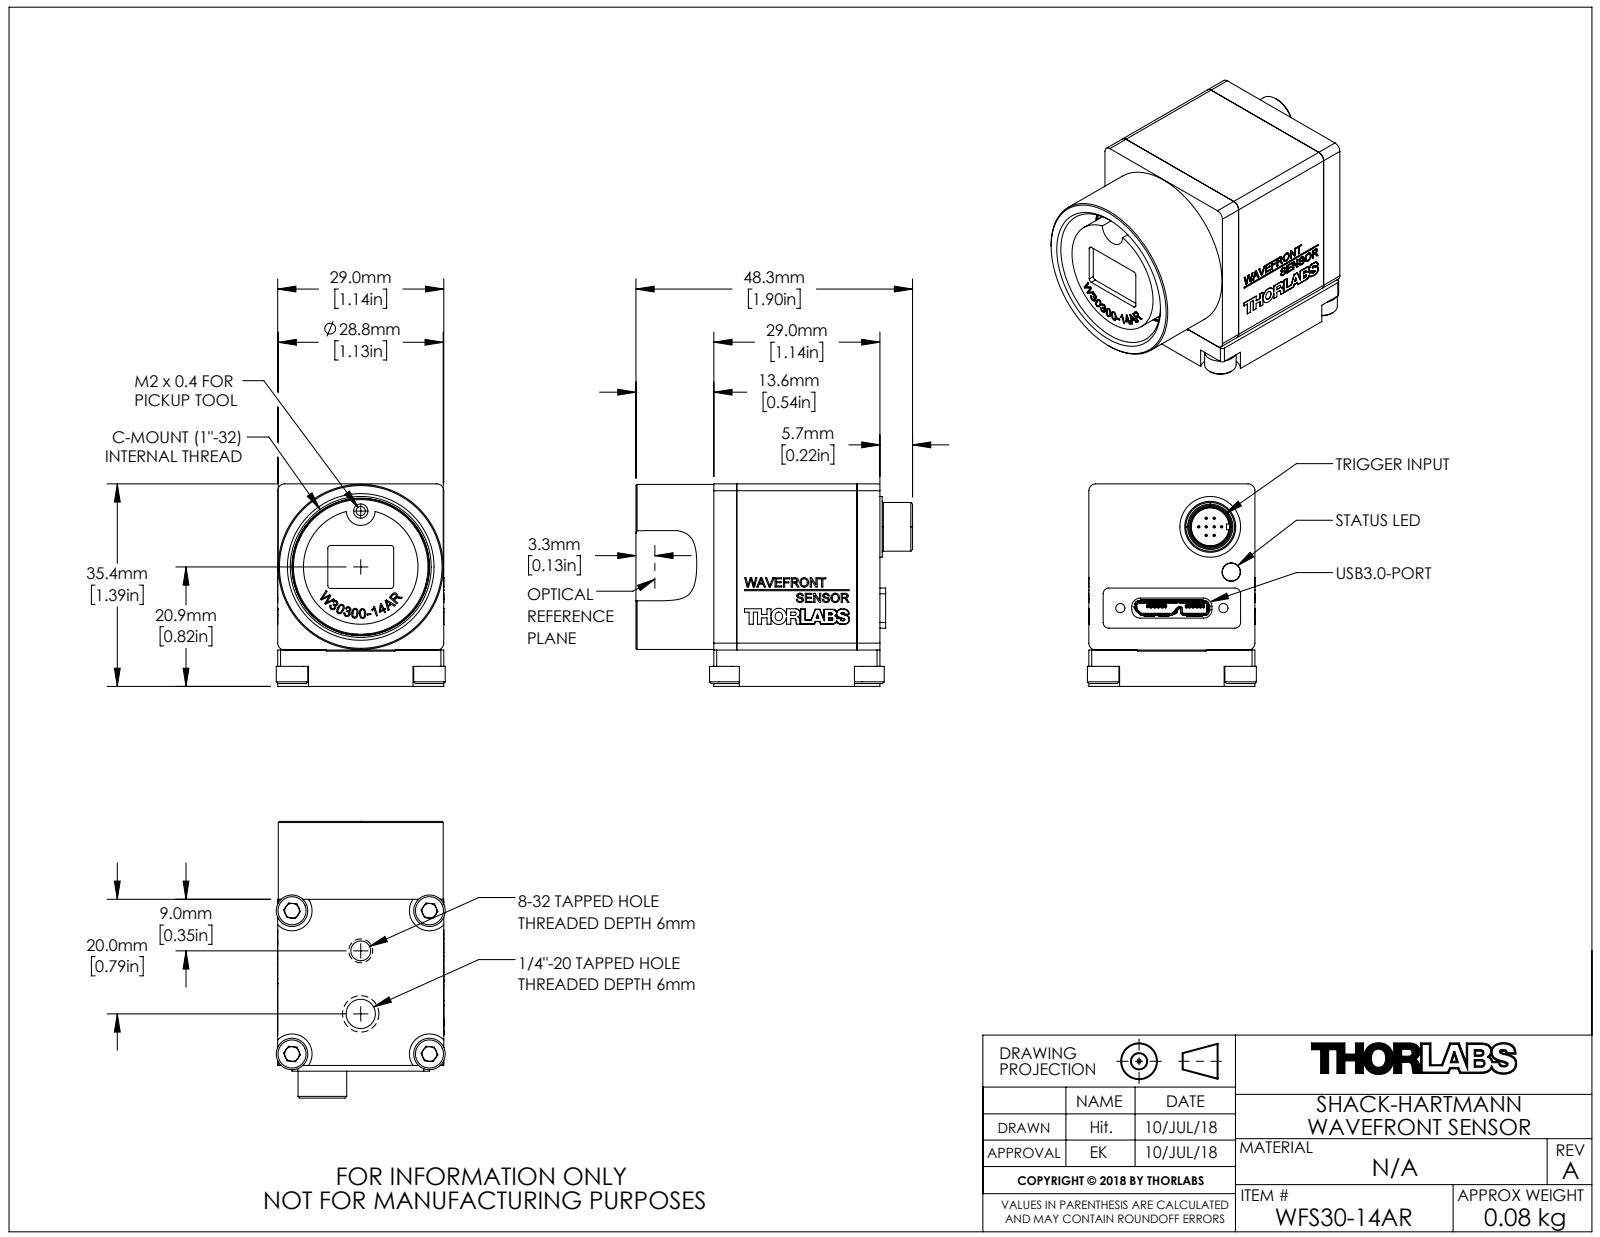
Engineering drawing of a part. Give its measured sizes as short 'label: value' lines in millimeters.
name: MTN008513-E0W
written by: SolidWorks 2016 (AUTOMOTIVE_DESIGN)
unit: mm
bodies: 0 solids, 2626 faces (1902 planar, 407 cylindrical, 317 other)
size: 48.3 × 35.35 × 29.5
holes: 11× ⌀3.2, 5× ⌀2.5, 3× ⌀1.6, 3× ⌀1.9, 1× ⌀0.95, 1× ⌀1.5, 1× ⌀3.45, 1× ⌀5.11, 1× ⌀6.8, 1× ⌀8, 1× ⌀15, 1× ⌀24
bosses: 8× ⌀0.4, 6× ⌀1, 5× ⌀3, 4× ⌀5.5, 1× ⌀28.8, 1× ⌀23.9, 1× ⌀23.5, 1× ⌀20
rounds: 31× R0.2, 29× R0.15, 29× R0.5, 12× R0.3, 11× R1, 10× R1.5, 8× R0.1, 8× R0.6
face distances: 29, 0.6, 28.4, 6.35, 4.8, 35.35, 2.62, 27.8, 17.57, 22.37
hole spacings: 9.75, 18.83, 9.74, 13.79, 16.88, 5.04, 13.89, 21.63
